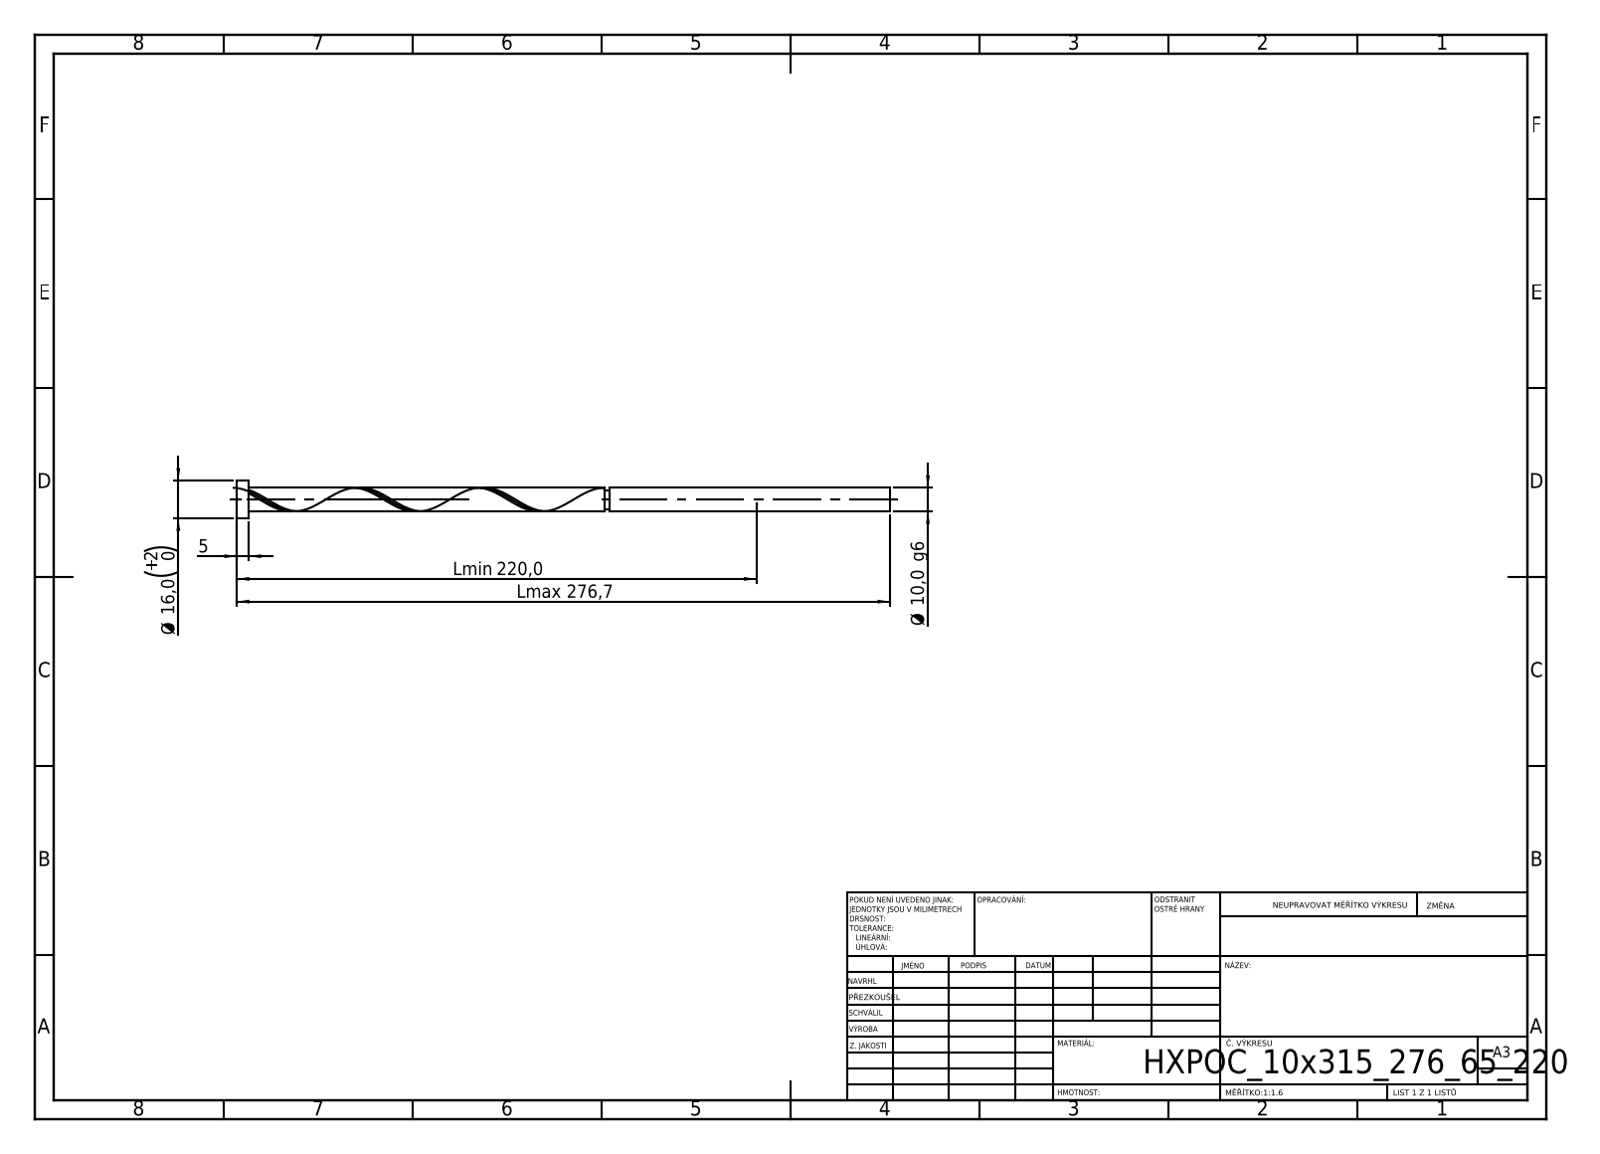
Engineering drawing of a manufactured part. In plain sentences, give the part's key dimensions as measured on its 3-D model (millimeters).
Its 3-D file was written by "SolidWorks 2019 (CONFIG_CONTROL_DESIGN)". It is 1 solid with 22 faces: 5 planar, 15 cylindrical and 2 other. Overall it measures 276.65 by 16 by 16 millimeters. Its volume is 22 050 cubic millimeters and its surface area 9 432 square millimeters. Round bosses or shafts: 1 of diameter 16, 1 of diameter 10, 1 of diameter 8. The main face-to-face distances are 5, 276.65, 271.65, 157.71, 152.71, 118.94, 155.71, 150.71, 2, 120.94.
